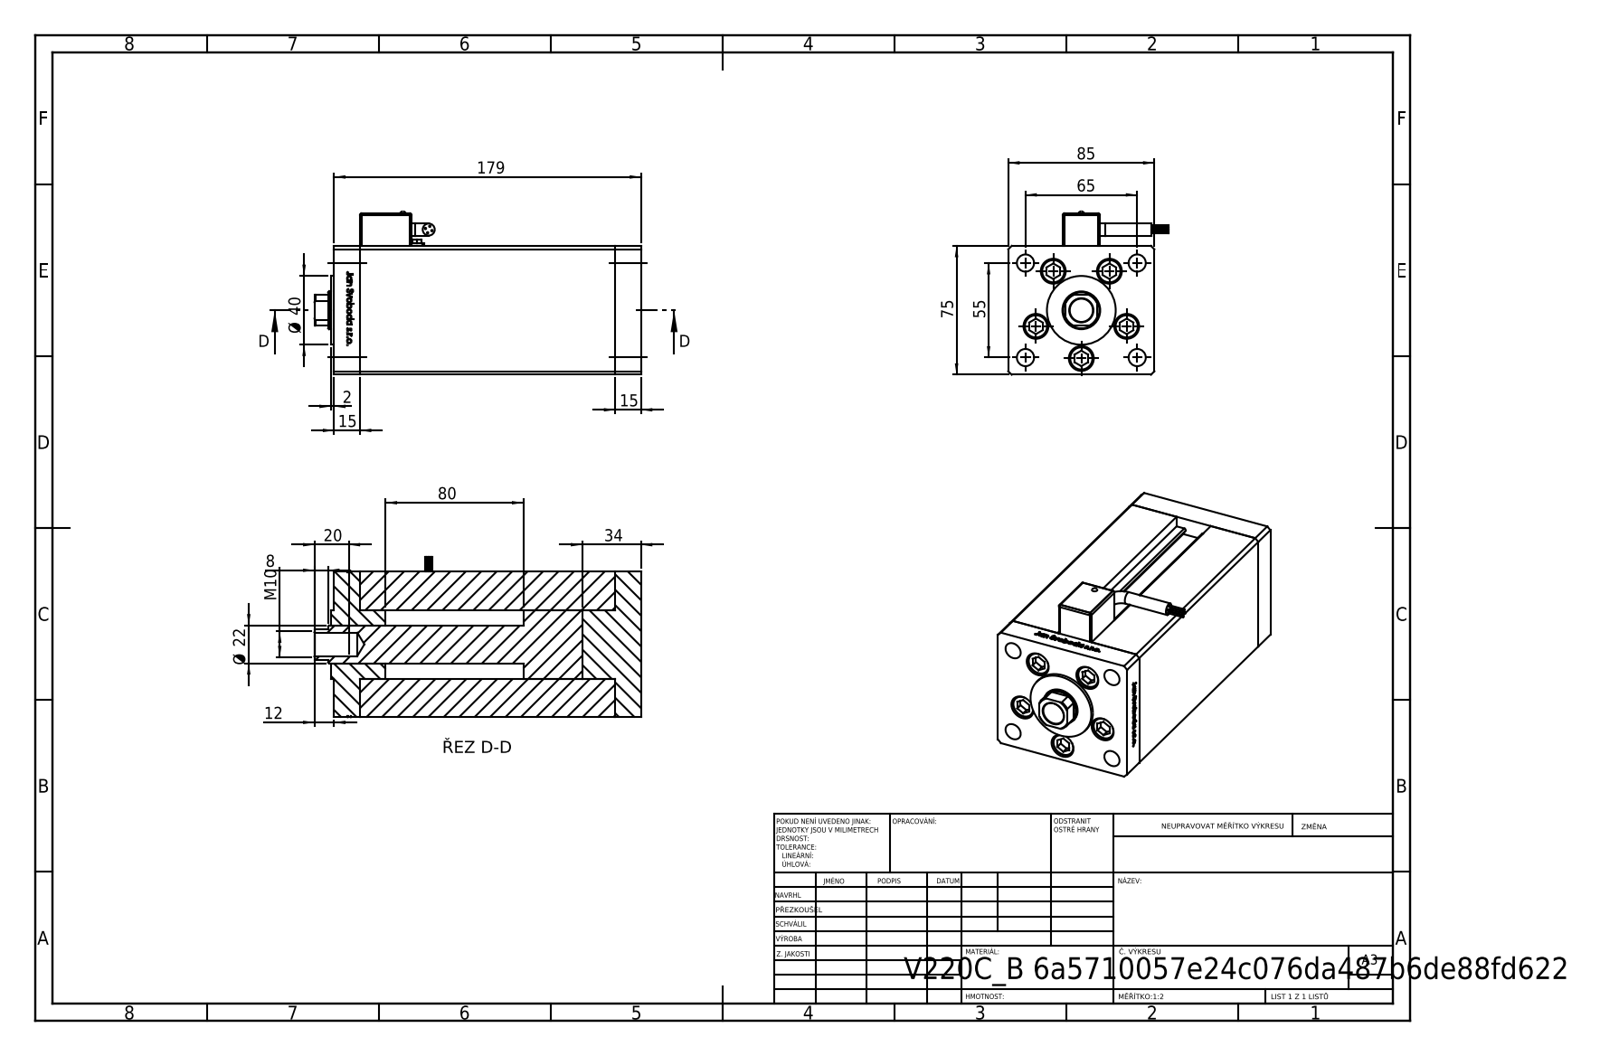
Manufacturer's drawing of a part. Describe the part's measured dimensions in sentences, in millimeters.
The part is named "V220C_B MIDDLE; V220C_VC_B; ALLEN BOLT; V220C_FRONT_B (+2 more)". Its 3-D file was written by "SolidWorks 2019 (CONFIG_CONTROL_DESIGN)". It is 15 solids with 1287 faces: 503 planar, 192 cylindrical and 592 other. Overall it measures 190 by 95.1 by 93.3 millimeters. Its volume is 1 030 000 cubic millimeters and its surface area 166 159 square millimeters. Round holes: 5 of diameter 11, 5 of diameter 14.5, 4 of diameter 10, 2 of diameter 2, 2 of diameter 13.16, 1 of diameter 3.6, 1 of diameter 5, 1 of diameter 7, 1 of diameter 13.5, 1 of diameter 22. Round bosses or shafts: 5 of diameter 8, 4 of diameter 0.85, 2 of diameter 7, 1 of diameter 40, 1 of diameter 6, 1 of diameter 3.5, 1 of diameter 2.5. Partial cylindrical surfaces (rounded edges, fillets, slot ends): 14 of radius 1, 2 of radius 0.93, 2 of radius 4, 1 of radius 10.5. The main face-to-face distances are 85, 75, 15, 148.5, 163.5, 178.5, 34.25, 68.5, 19.25, 129.25. The hole center spacings are 28, 42.57, 16.86, 19.17, 32.33, 32.5, 33.63, 37.33.
